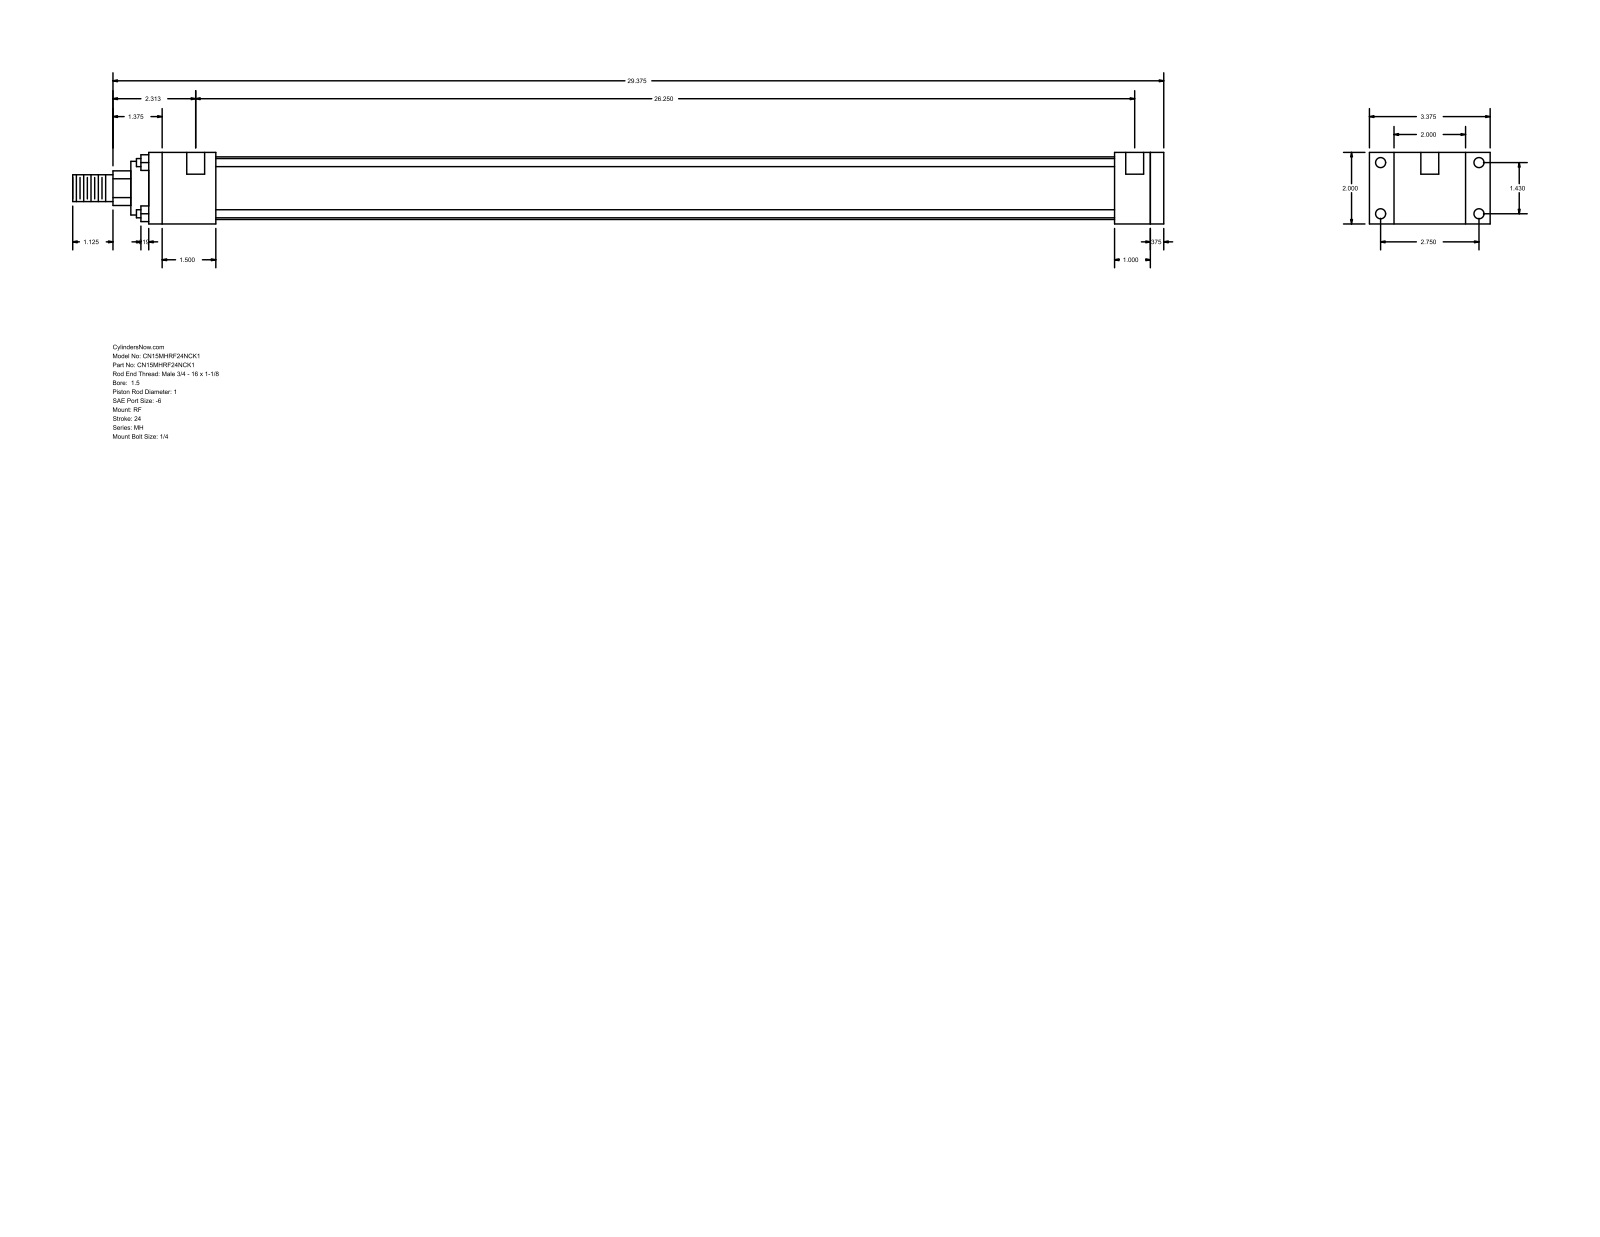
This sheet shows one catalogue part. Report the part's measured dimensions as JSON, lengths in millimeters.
{"part_name": "MH_RF__0150_1", "step_written_by": "GSSL Pune (CONFIG_CONTROL_DESIGN)", "units": "millimeters", "bodies": {"solids": 0, "faces": 92, "planar": 64, "cylindrical": 28, "other": 0}, "overall_size": [774.7, 85.72, 50.8], "round_holes": [[5.56, 4], [7.14, 4], [12.7, 2]], "round_bosses_or_shafts": [[5.71, 4], [44.45, 1], [38.1, 1], [25.4, 1], [19.05, 1]], "partial_cylinders_radius": [[12.29, 1]], "face_to_face_distances": [50.8, 9.52, 711.2, 25.4, 720.72, 17.46, 68.26, 685.8, 34.92, 47.63], "hole_center_spacings": [36.32, 69.84, 78.72, 669.93, 3.18, 666.75]}
